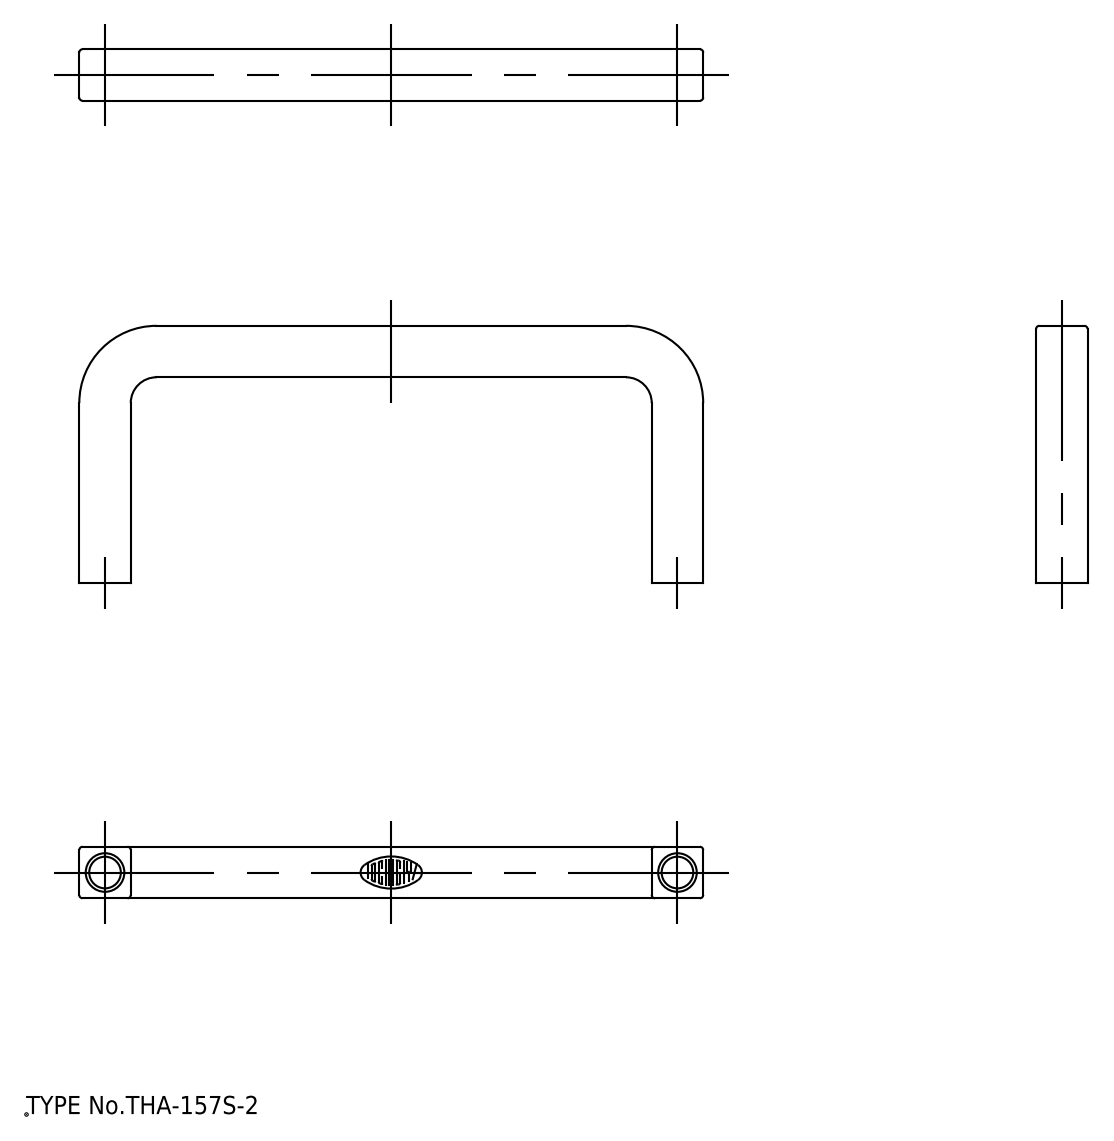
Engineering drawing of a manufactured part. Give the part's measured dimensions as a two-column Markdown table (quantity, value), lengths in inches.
| quantity | value |
| --- | --- |
| STEP written by | spGate 19.8.4 (****-****-****-****) (AUTOMOTIVE_DESIGN) |
| units | inches |
| bodies | 1 solid, 40 faces (12 planar, 20 cylindrical, 8 other) |
| overall size | 3.819 × 1.575 × 0.315 |
| volume | 0.565 in³ |
| surface area | 8.223 in² |
| round holes (diameter × count) | 0.236 × 2 |
| partial cylindrical surfaces (radius × count) | 0.02 × 12, 0.157 × 2, 0.472 × 2 |
| main face-to-face distances | 0.315, 3.504, 3.819, 3.189, 1.26, 1.575, 0.394, 0.866, 1.181 |
| hole center spacings | 3.504 |
